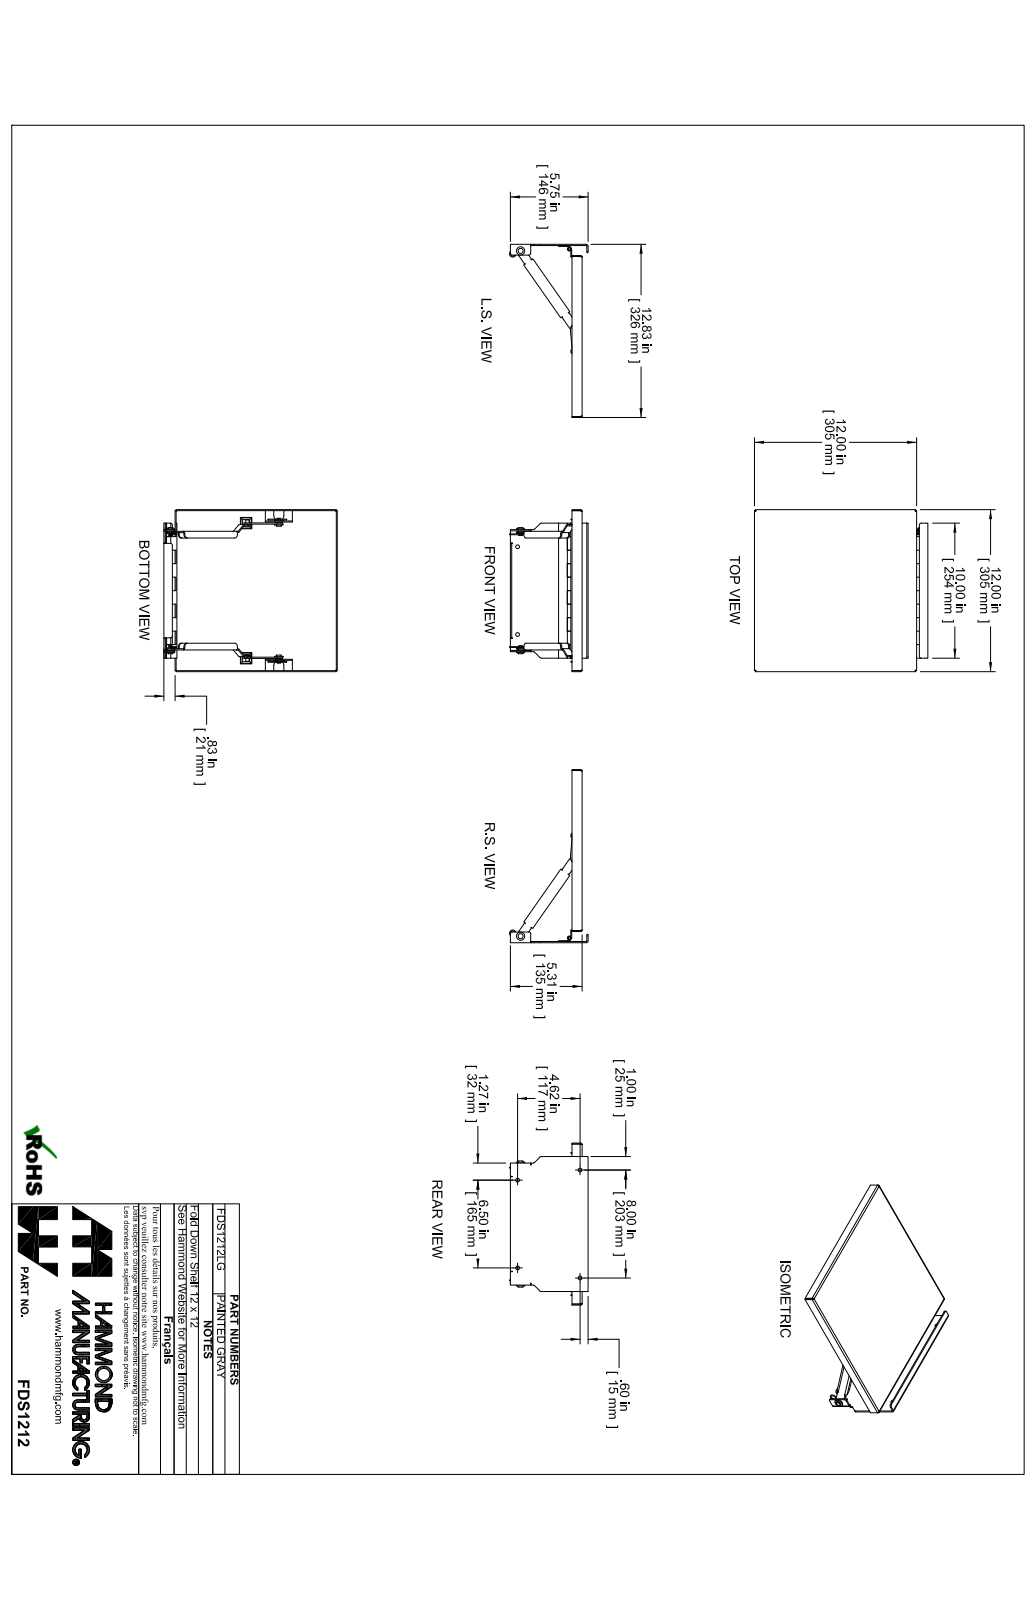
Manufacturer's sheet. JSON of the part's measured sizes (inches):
{"part_name": "FDS1212LG", "step_written_by": "SolidWorks 2019 (CONFIG_CONTROL_DESIGN)", "units": "inches", "bodies": {"solids": 15, "faces": 345, "planar": 218, "cylindrical": 115, "other": 12}, "overall_size": [12.831, 12, 5.75], "volume_in3": 22.53, "surface_area_in2": 594.9, "round_holes": [[0.281, 4], [0.257, 2], [0.265, 2], [0.265, 2], [0.187, 1], [0.2, 1], [0.26, 1]], "round_bosses_or_shafts": [[0.51, 1], [0.5, 1], [0.32, 1], [0.25, 1]], "partial_cylinders_radius": [[0.25, 12], [0.048, 10], [0.125, 10], [0.143, 10], [0.036, 6], [0.108, 6], [0.375, 2]], "face_to_face_distances": [0.072, 0.095, 11.928, 0.095, 11.856, 12, 0.625, 0.808, 0.903, 0.06], "hole_center_spacings": [8.6, 0.111, 2.256, 2.367, 3.535, 4.685, 4.685, 5.913]}
